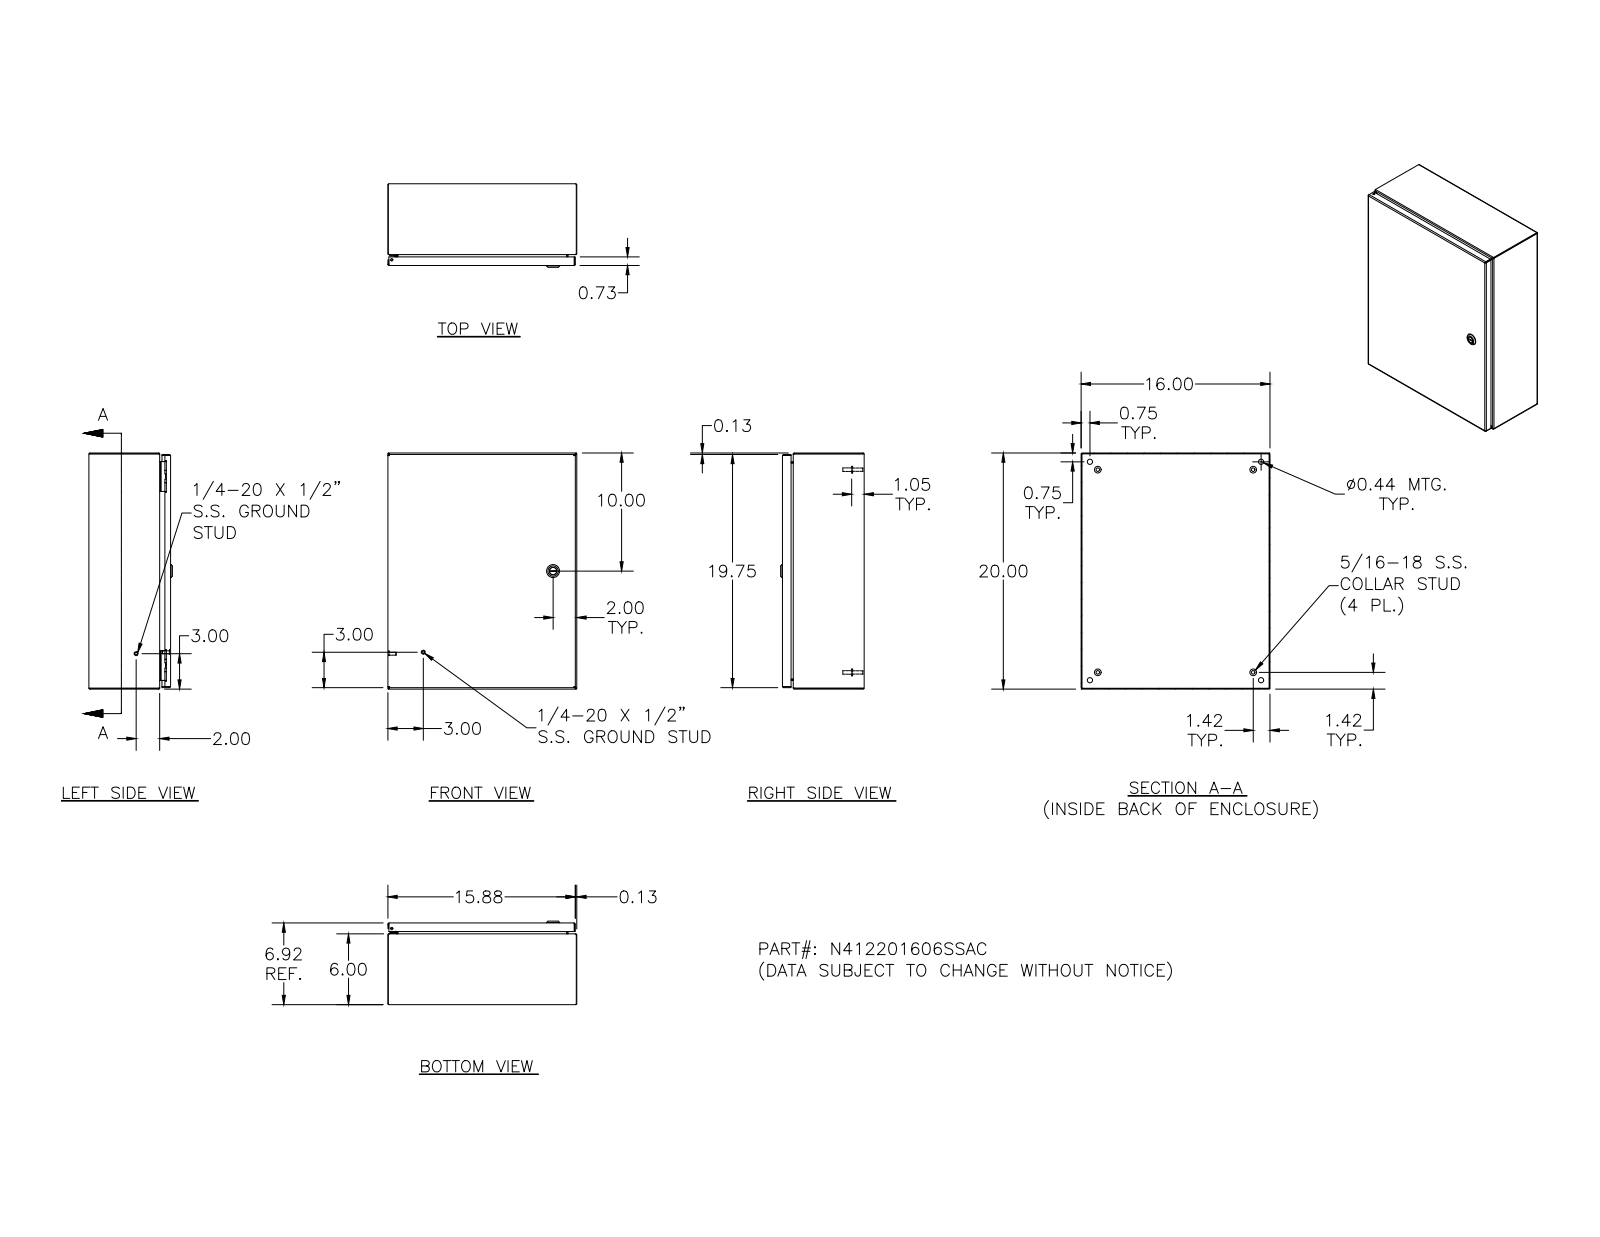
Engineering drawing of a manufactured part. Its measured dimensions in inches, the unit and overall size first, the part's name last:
Units: inches
Overall size (bounding box): 20 × 16 × 7.075
Round holes (diameter × count): ⌀0.188 ×5, ⌀0.093 ×4, ⌀0.152 ×4, ⌀0.167 ×4, ⌀0.172 ×4, ⌀0.437 ×4, ⌀0.156 ×2, ⌀0.187 ×1, ⌀0.197 ×1, ⌀0.315 ×1, ⌀0.394 ×1, ⌀0.402 ×1
Round bosses / shafts (diameter × count): ⌀0.25 ×10, ⌀0.563 ×4, ⌀0.36 ×4, ⌀0.32 ×4, ⌀0.3 ×4, ⌀0.275 ×4, ⌀0.256 ×4, ⌀0.164 ×4
Partial cylindrical surfaces — rounded edges, fillets, slot ends (radius × count): R0.05 ×26, R0.016 ×18, R0.016 ×16, R0.09 ×16, R0.031 ×14, R0.125 ×14, R0.02 ×9, R0.032 ×8
Main face-to-face distances: 0.074, 6.843, 6.769, 6.917, 15.926, 19.926, 16, 15.852, 20, 19.852
Hole centre spacings: 16, 0.017, 0.66, 16.008, 0.019, 0.5, 0.648, 0.652
Volume: 90.48 in³ · Surface area: 2 462 in²
Bodies: 34 solids, 1364 faces (523 planar, 497 cylindrical, 344 other)
Part name (STEP PRODUCT): N412201606SSAC; N412201606SSACBKP; 388151; N4122016SSACLID (+8 more)
STEP written by: Autodesk Inventor 2011 (AUTOMOTIVE_DESIGN)
